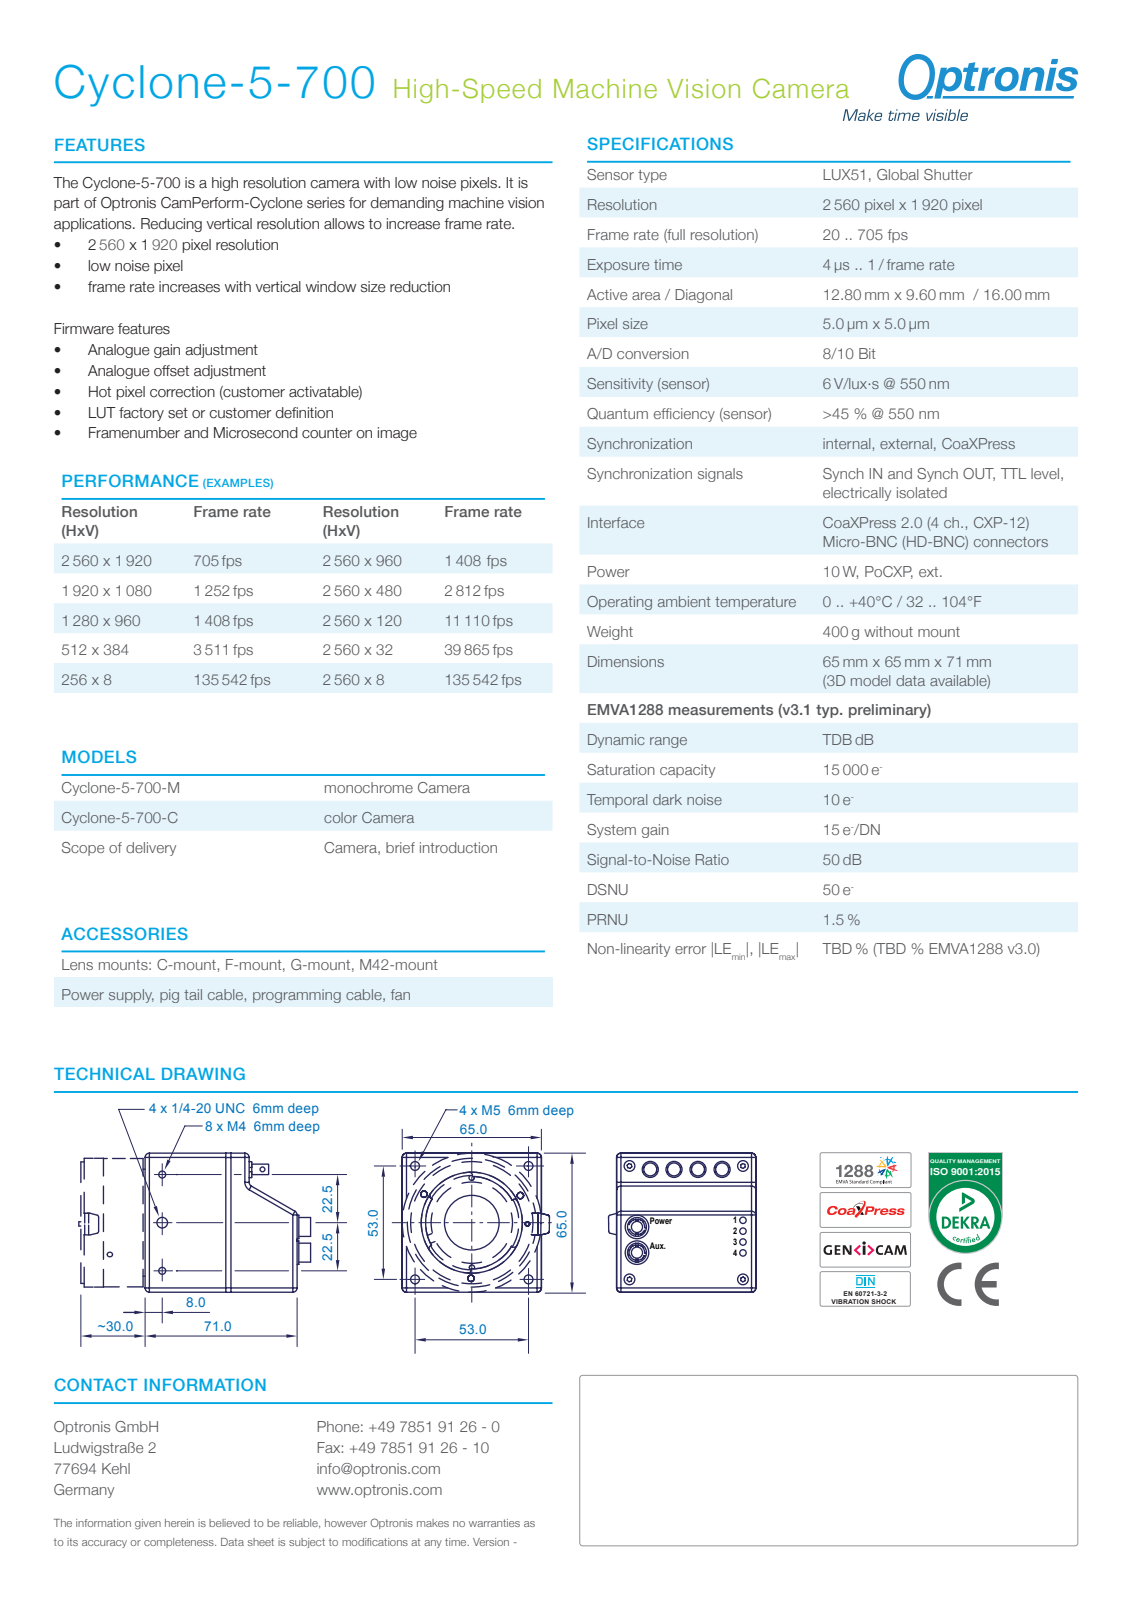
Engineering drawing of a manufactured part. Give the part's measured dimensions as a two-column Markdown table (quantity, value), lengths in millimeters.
| quantity | value |
| --- | --- |
| part name | 1200-MG-01-D_Cyclone |
| STEP written by | Autodesk Inventor 2026 (AUTOMOTIVE_DESIGN) |
| units | millimeters |
| bodies | 7 solids, 3391 faces (1730 planar, 1146 cylindrical, 515 other) |
| overall size | 77.3 × 65.02 × 65 |
| volume | 85 904 mm³ |
| surface area | 67 489 mm² |
| round holes (diameter × count) | 0.8 × 18, 0.5 × 10, 1.57 × 8, 0.45 × 4, 0.46 × 4, 2.7 × 4, 2.8 × 4, 3.05 × 4, 3.24 × 4, 3.59 × 4, 3.6 × 4, 4 × 4 |
| round bosses / shafts (diameter × count) | 0.86 × 209, 0.3 × 209, 1.1 × 10, 7.5 × 4, 6.32 × 4, 5.2 × 4, 4.55 × 4, 4.5 × 4 |
| partial cylindrical surfaces (radius × count) | 3 × 32, 1 × 28, 2 × 22, 0.5 × 12, 0.2 × 10, 0.45 × 10, 0.16 × 8, 2.1 × 4 |
| main face-to-face distances | 2, 63, 65, 61, 3, 59, 0.5, 28.4, 25.4, 27.9 |
| hole center spacings | 1.8, 3.12, 53, 1.6, 2.26, 11.2, 22.5, 37.48 |
